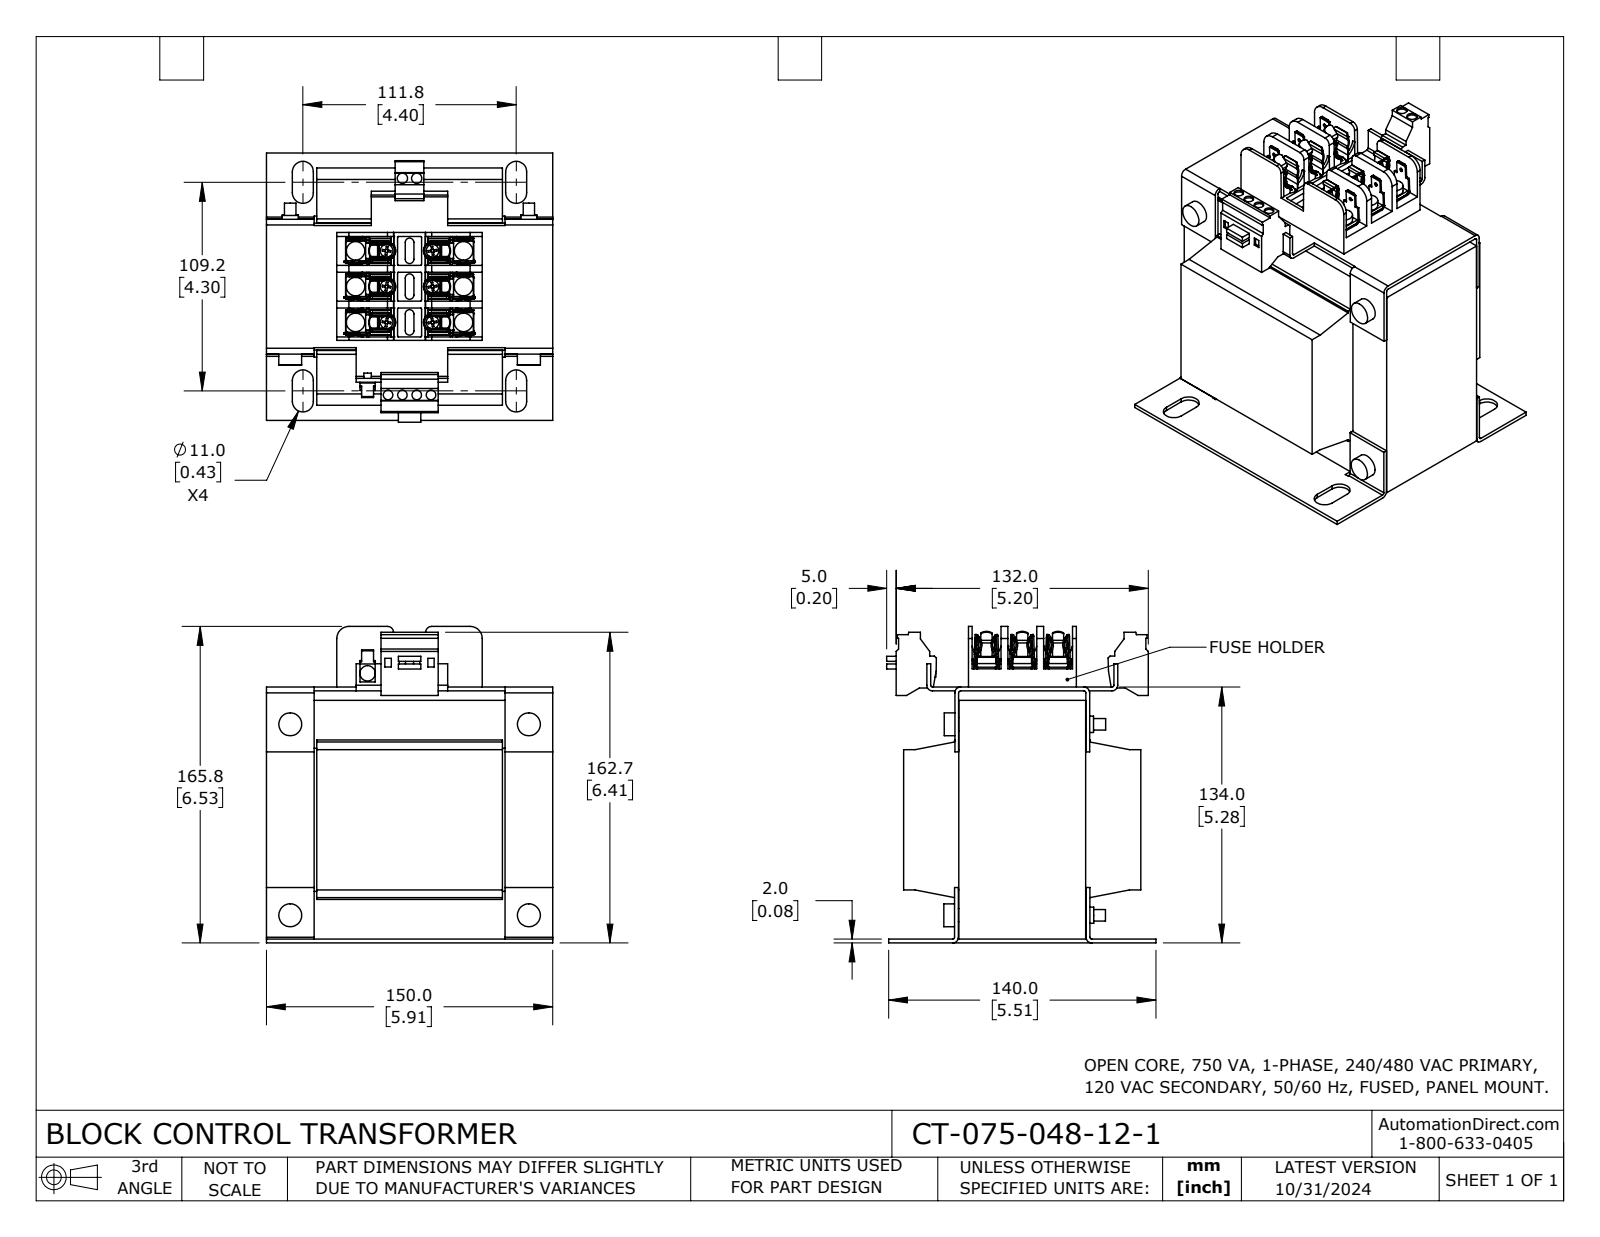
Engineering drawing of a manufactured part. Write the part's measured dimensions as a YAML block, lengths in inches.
part_name: "CT-075-048-12-1"
step_written_by: "SolidWorks 2023 (CONFIG_CONTROL_DESIGN)"
units: inches
bodies: {solids: 2, faces: 1586, planar: 1025, cylindrical: 531, other: 30}
overall_size: [6.526, 5.906, 5.551]
volume: 111.2
surface_area: 363.8
round_holes:
  - {diameter: 0.074, count: 12}
  - {diameter: 0.205, count: 5}
  - {diameter: 0.197, count: 4}
  - {diameter: 0.213, count: 2}
  - {diameter: 0.205, count: 1}
round_bosses_or_shafts:
  - {diameter: 0.38, count: 6}
  - {diameter: 0.19, count: 6}
  - {diameter: 0.472, count: 4}
  - {diameter: 0.335, count: 4}
  - {diameter: 0.276, count: 4}
  - {diameter: 0.236, count: 4}
  - {diameter: 0.315, count: 1}
  - {diameter: 0.157, count: 1}
partial_cylinders:
  - {radius: 0.01, count: 24}
  - {radius: 0.05, count: 20}
  - {radius: 0.03, count: 18}
  - {radius: 0.072, count: 14}
  - {radius: 0.038, count: 12}
  - {radius: 0.04, count: 12}
  - {radius: 0.164, count: 12}
  - {radius: 0.097, count: 9}
face_to_face_distances: [0.079, 5.197, 4.921, 1.039, 4.866, 0.984, 5.276, 1.138, 3.756, 3.937]
hole_center_spacings: [2.232, 2.354, 0.026, 0.026, 0.052, 0.295, 0.738, 1.779]
